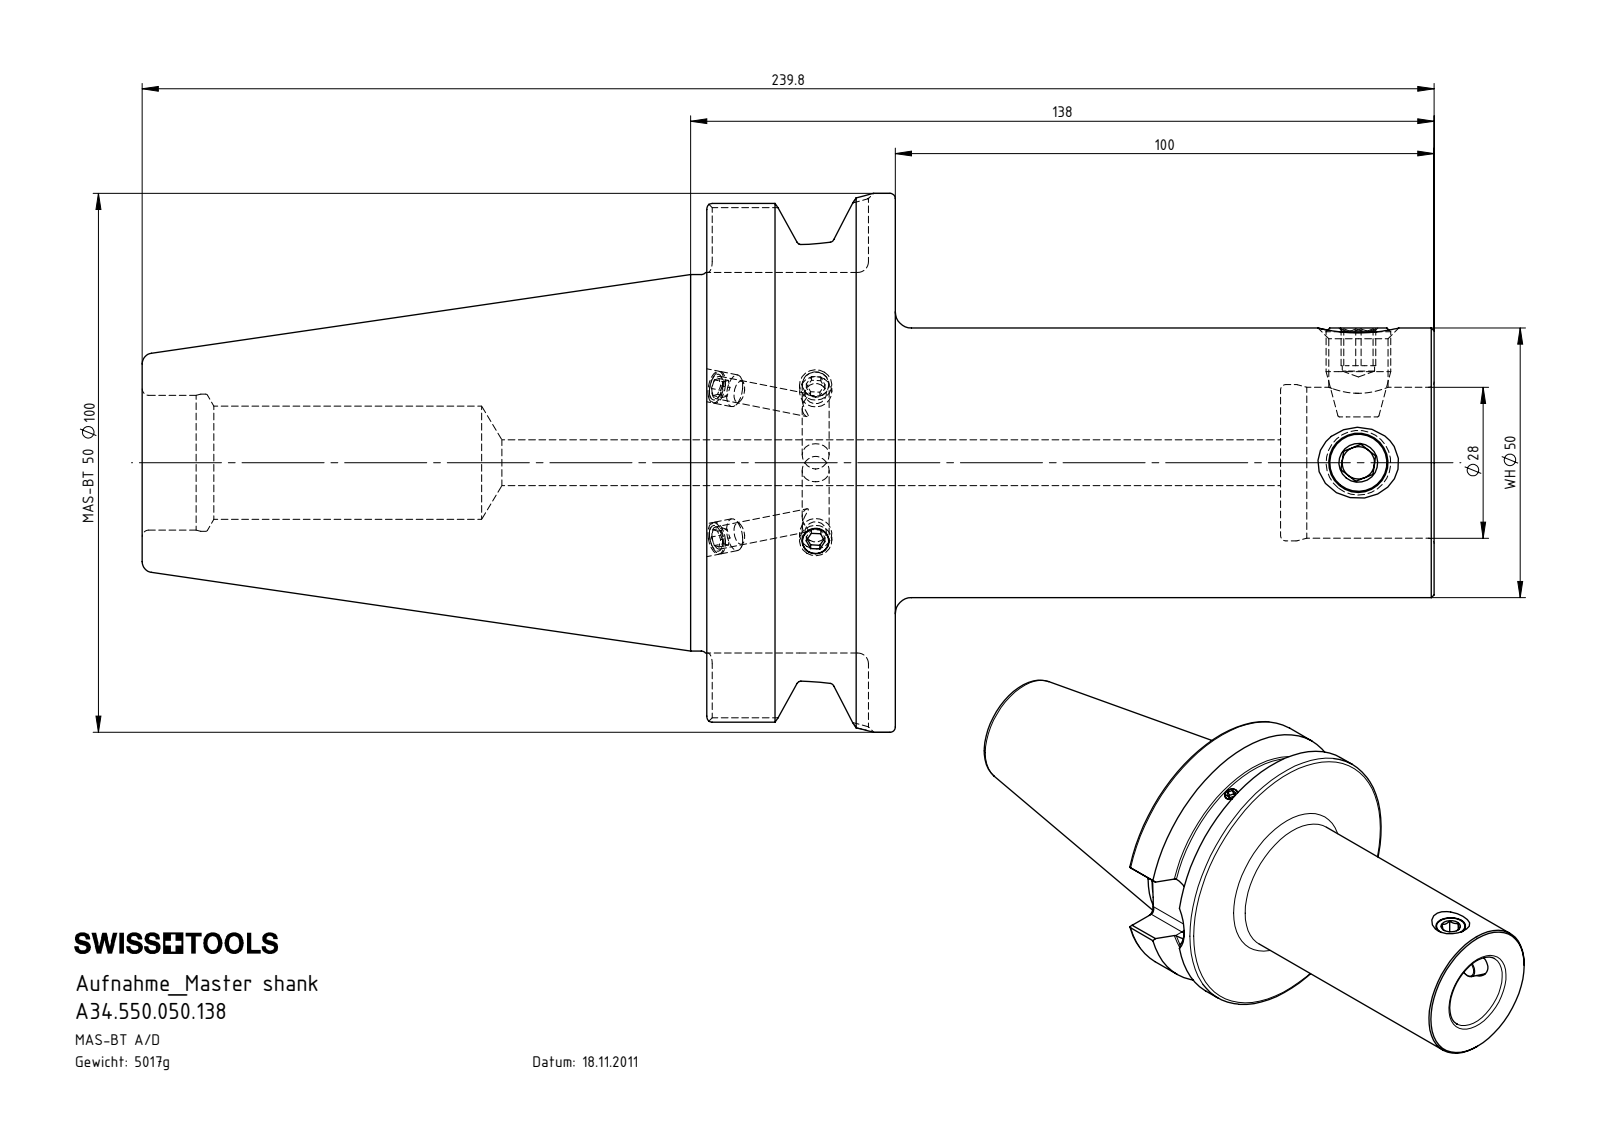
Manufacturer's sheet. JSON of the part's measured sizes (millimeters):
{"part_name": "A34.550.050.138; ISO 4026 - M6 x 5_PreviewCfg; BB5-WH5.K01.138_C; WH5-ER1.001.017", "step_written_by": "SolidWorks 2017 (CONFIG_CONTROL_DESIGN)", "units": "millimeters", "bodies": {"solids": 7, "faces": 240, "planar": 84, "cylindrical": 65, "other": 91}, "overall_size": [239.8, 100, 100], "volume_mm3": 639496, "surface_area_mm2": 74729, "round_holes": [[6, 4], [4.2, 2], [11, 2], [5, 1], [8.5, 1], [21, 1], [25, 1], [25.45, 1], [28, 1], [29, 1]], "round_bosses_or_shafts": [[12, 2], [6, 2], [100, 1], [85, 1], [69.85, 1], [50, 1]], "partial_cylinders_radius": [[2, 8], [12.85, 1]], "face_to_face_distances": [35, 135, 100, 70.6, 106.5, 71.5, 28.5, 104.8, 139.8, 211.3]}
